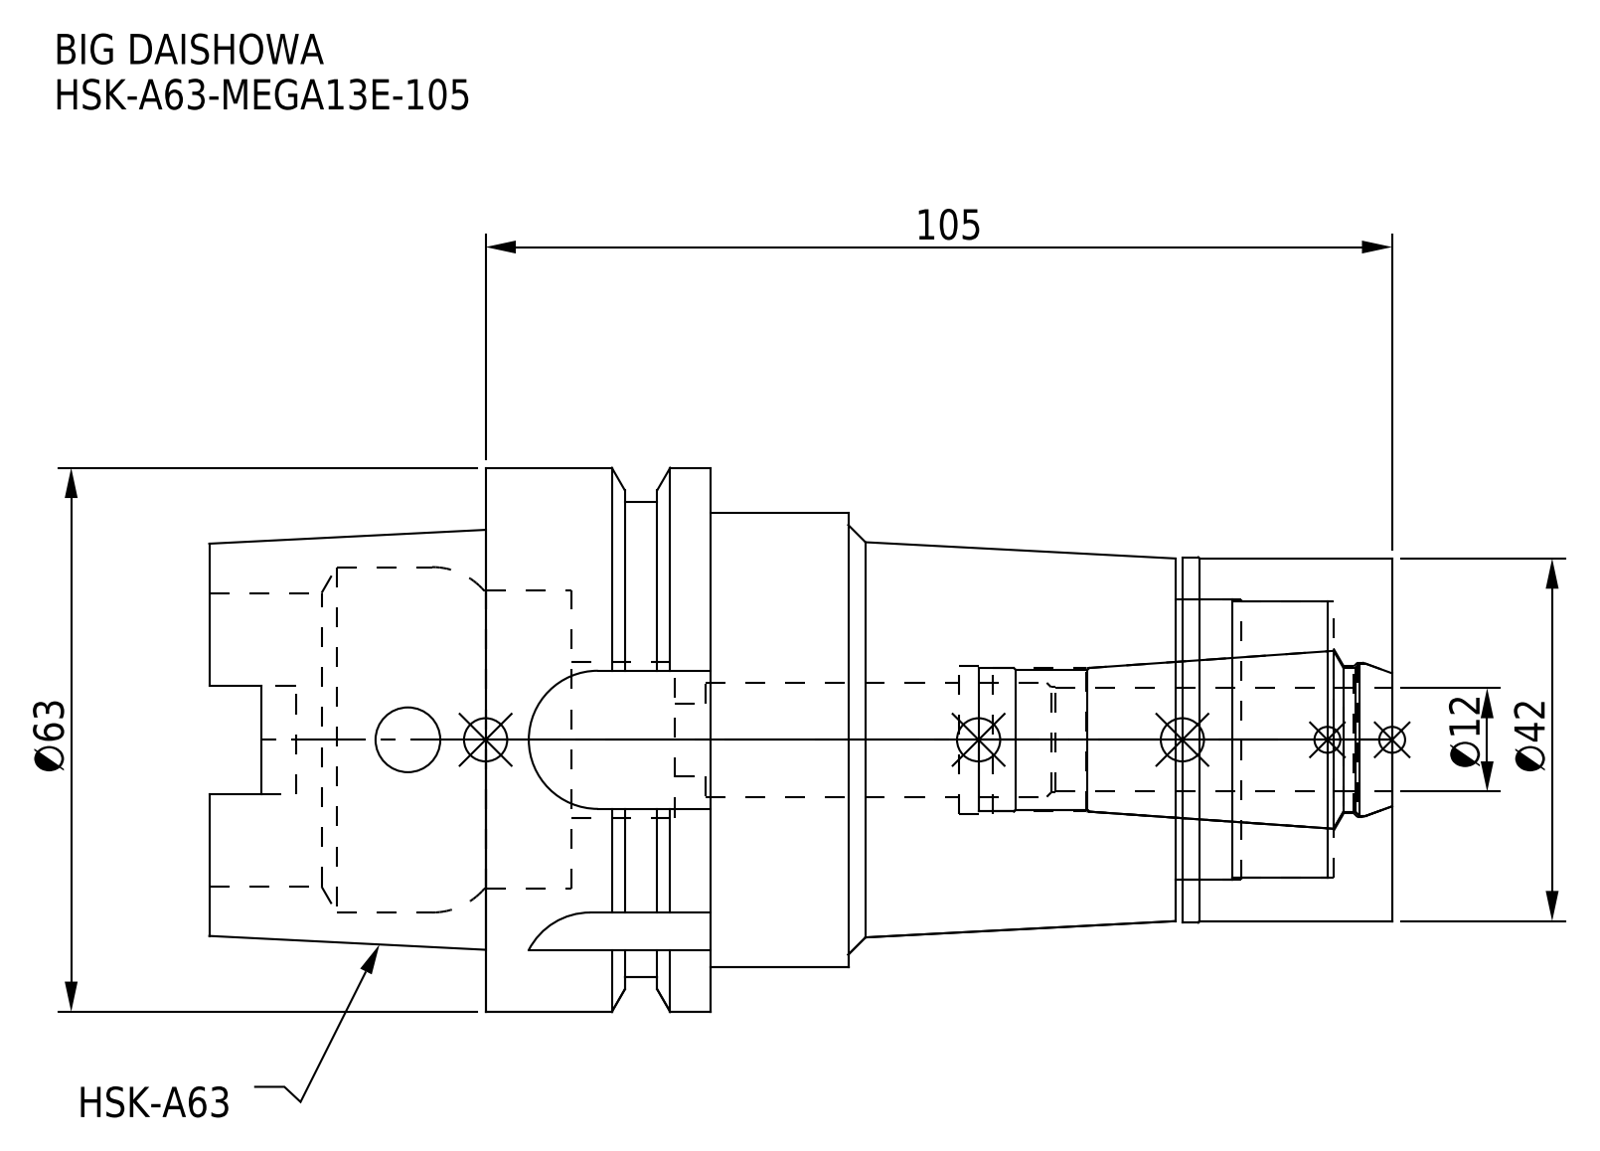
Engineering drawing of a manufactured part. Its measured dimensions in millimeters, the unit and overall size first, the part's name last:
Units: millimetres
Overall size (bounding box): 137 × 63 × 63
Round holes (diameter × count): ⌀7.5 ×1, ⌀8.4 ×1, ⌀13.3 ×1, ⌀16.6 ×1, ⌀17 ×1, ⌀17.2 ×1, ⌀17.9 ×1, ⌀18 ×1, ⌀32 ×1, ⌀32.5 ×1, ⌀34 ×1, ⌀34.5 ×1
Round bosses / shafts (diameter × count): ⌀63 ×1, ⌀55 ×1, ⌀52.6 ×1, ⌀42.3 ×1, ⌀42 ×1
Partial cylindrical surfaces — rounded edges, fillets, slot ends (radius × count): R2.8 ×2, R2.88 ×2, R8 ×2, R9 ×1
Main face-to-face distances: 105, 26, 79, 95.05, 16.05, 9.95, 25.1, 24.3, 54.7, 70.75
Volume: 191 632 mm³ · Surface area: 42 802 mm²
Bodies: 2 solids, 127 faces (45 planar, 54 cylindrical, 28 other)
Part name (STEP PRODUCT): HSK-A63-MEGA13E-105-120-FreeParts; HSK-A63-MEGA13E-105-120.stp; HSK-A63-MEGA13E-105; MEN13_1.stp (+3 more)
STEP written by: SolidWorks 2019 (CONFIG_CONTROL_DESIGN)
